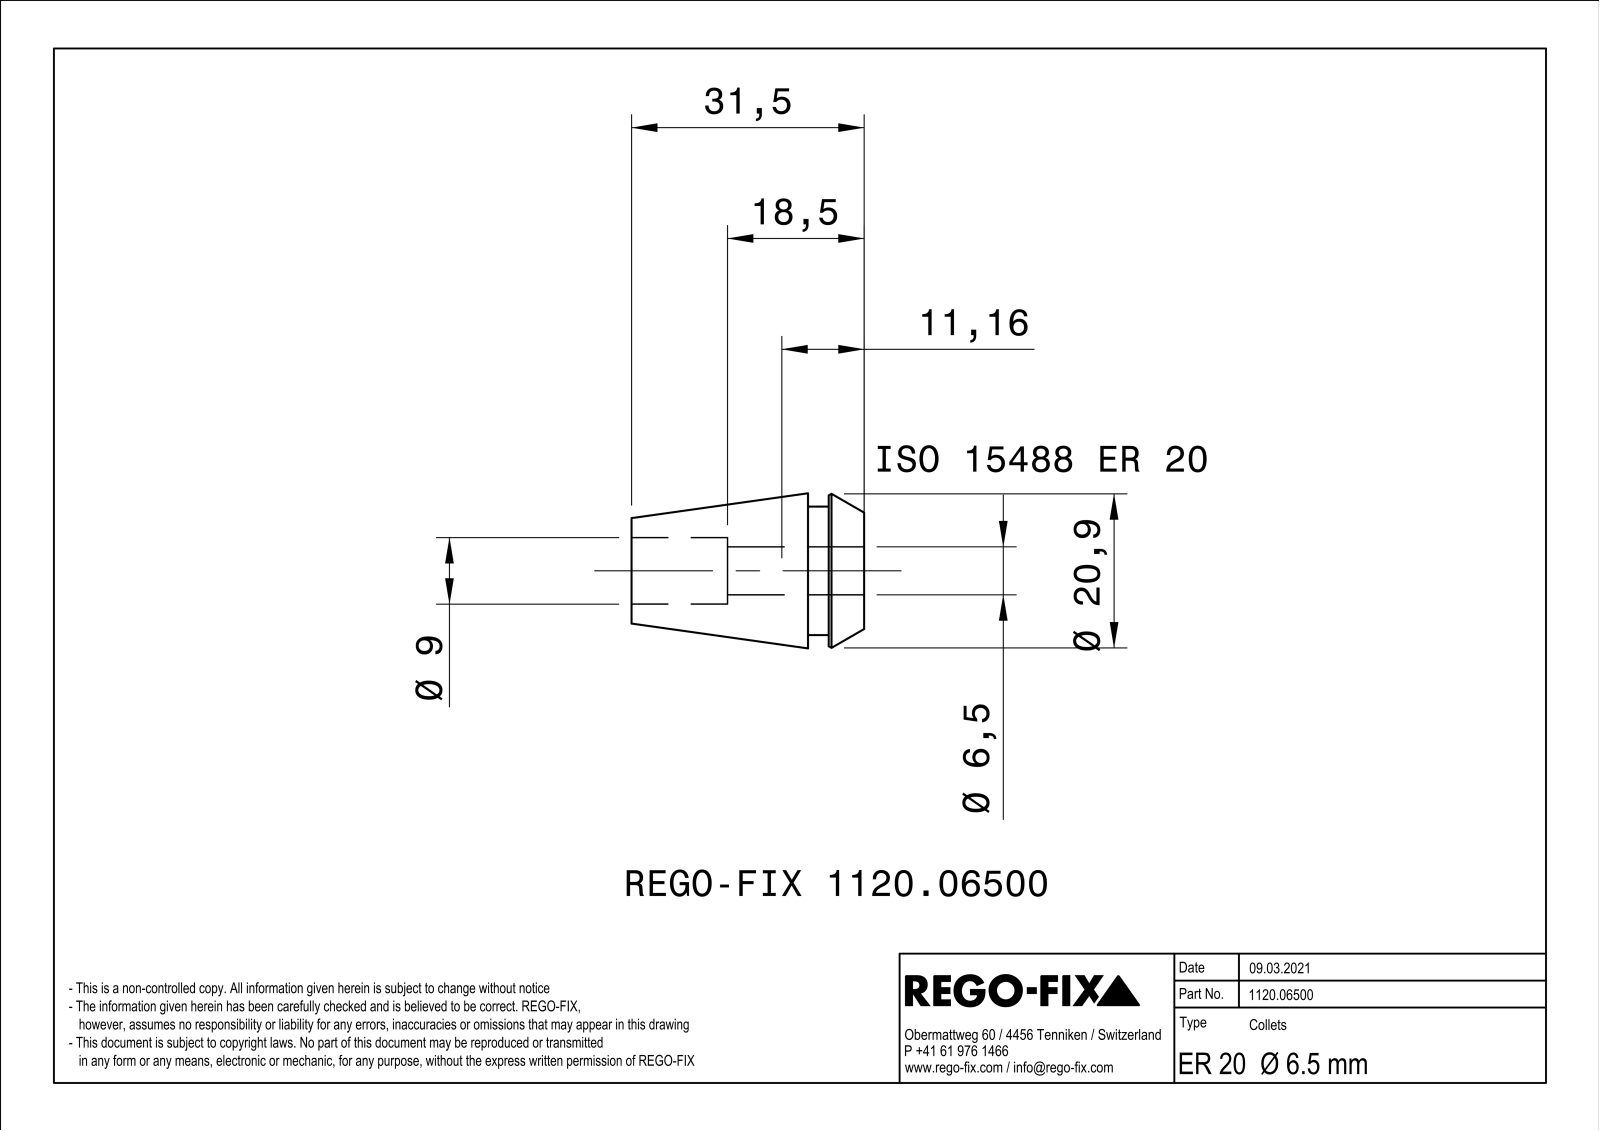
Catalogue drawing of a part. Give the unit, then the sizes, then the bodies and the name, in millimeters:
Units: millimetres
Overall size (bounding box): 31.5 × 20.99 × 20.99
Round holes (diameter × count): ⌀9 ×1
Round bosses / shafts (diameter × count): ⌀17.4 ×1
Partial cylindrical surfaces — rounded edges, fillets, slot ends (radius × count): R40 ×8, R3.25 ×1
Main face-to-face distances: 0.6, 0.62, 0.58, 7.6, 4.8, 2.8, 31.5, 26.7, 23.9, 27
Volume: 5 288 mm³ · Surface area: 6 380 mm²
Bodies: 1 solid, 257 faces (104 planar, 41 cylindrical, 112 other)
Part name (STEP PRODUCT): NOCUT
STEP written by: SIEMENS PLM Software Solid Edge ST10 (AUTOMOTIVE_DESIGN)
